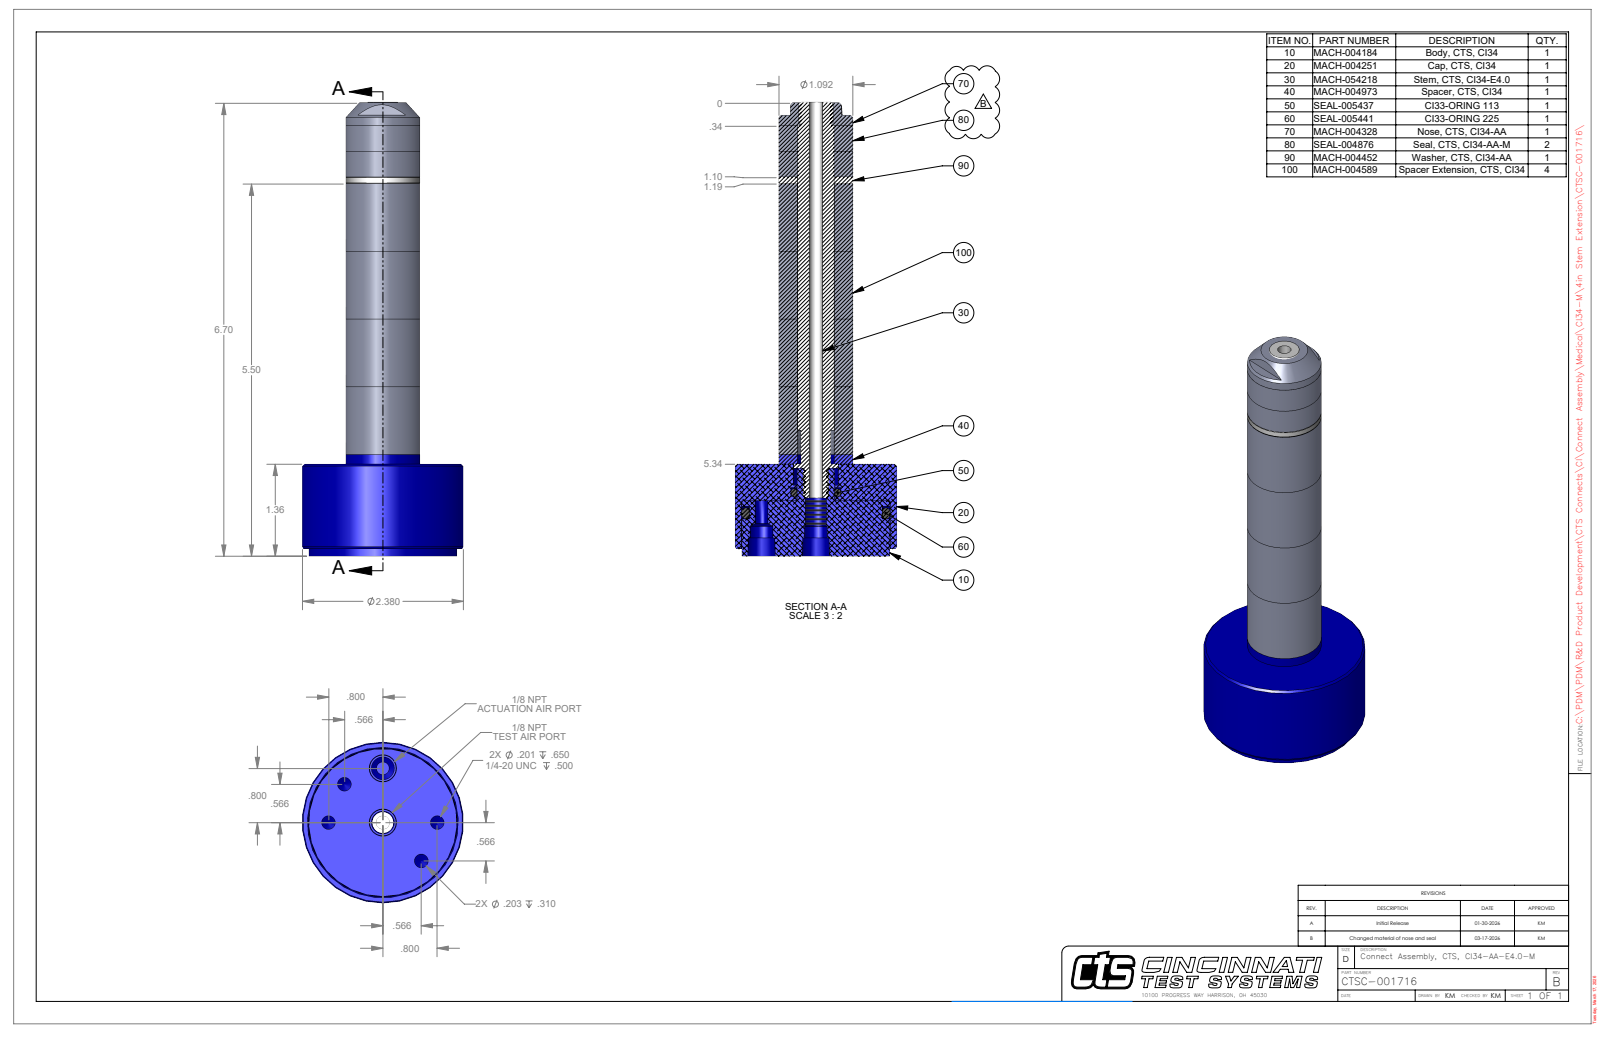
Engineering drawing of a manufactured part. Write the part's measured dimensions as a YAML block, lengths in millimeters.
part_name: "CTSC-001716"
step_written_by: "SolidWorks 2023 (AUTOMOTIVE_DESIGN)"
units: millimeters
bodies: {solids: 10, faces: 86, planar: 41, cylindrical: 32, other: 13}
overall_size: [170.33, 60.45, 60.45]
volume: 172583
surface_area: 47058
round_holes:
  - {diameter: 5.11, count: 2}
  - {diameter: 5.16, count: 2}
  - {diameter: 5.16, count: 1}
  - {diameter: 7.94, count: 1}
  - {diameter: 8.61, count: 1}
  - {diameter: 10.72, count: 1}
  - {diameter: 13.46, count: 1}
  - {diameter: 13.74, count: 1}
  - {diameter: 16.79, count: 1}
  - {diameter: 55.58, count: 1}
round_bosses_or_shafts:
  - {diameter: 60.45, count: 1}
  - {diameter: 55.32, count: 1}
  - {diameter: 27.74, count: 1}
  - {diameter: 27.69, count: 1}
  - {diameter: 16.51, count: 1}
  - {diameter: 13.44, count: 1}
  - {diameter: 12.7, count: 1}
face_to_face_distances: [25.4, 50.8, 34.54, 76.2, 161.47, 126.93, 151.82, 117.28, 9.65, 38.18]
hole_center_spacings: [20.32, 15.55, 37.55, 40.64]
